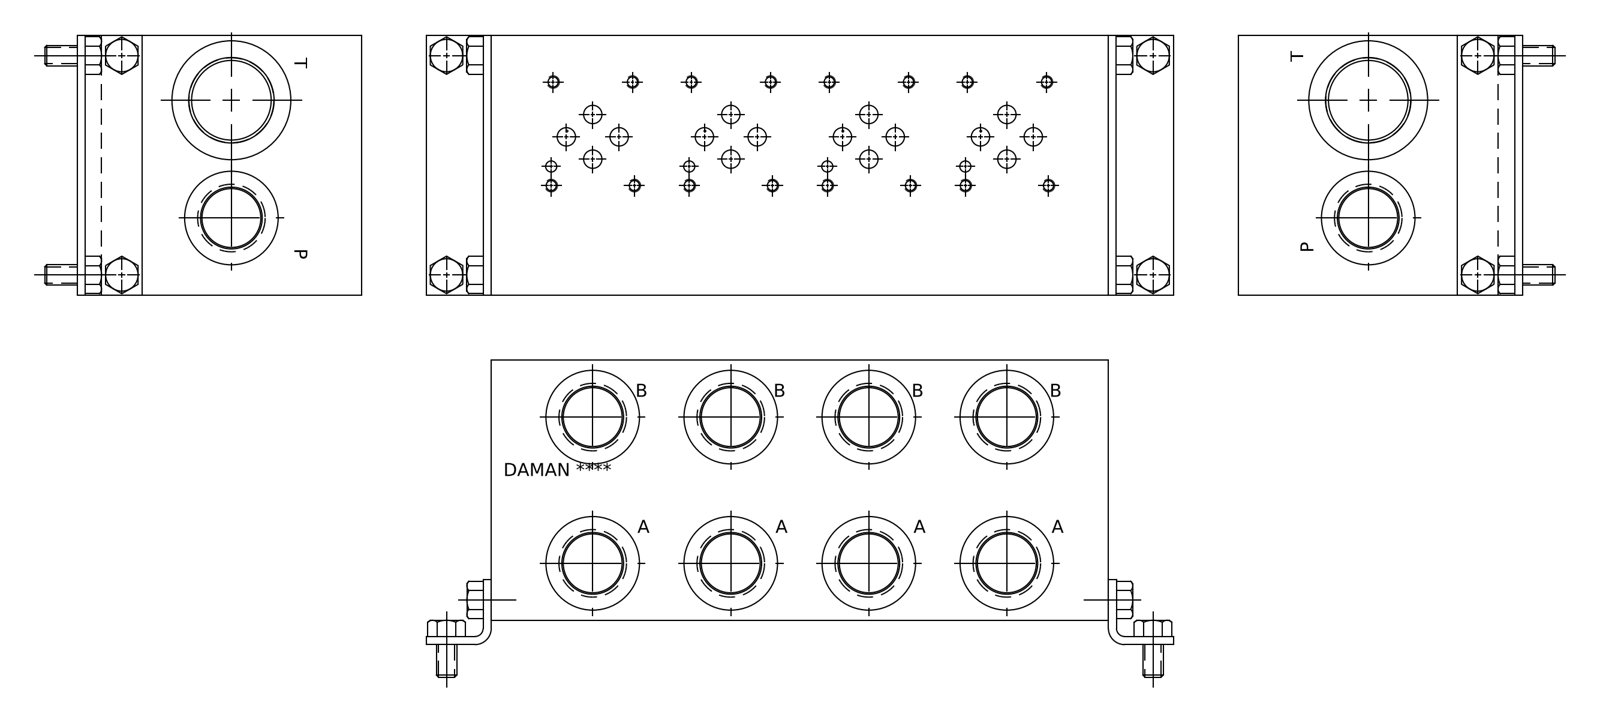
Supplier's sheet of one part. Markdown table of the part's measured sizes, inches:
| quantity | value |
| --- | --- |
| part name | Part_DD03HP042B_3D |
| STEP written by | Autodesk Inventor 2019 (AUTOMOTIVE_DESIGN) |
| units | inches |
| bodies | 1 solid, 770 faces (426 planar, 112 cylindrical, 232 other) |
| overall size | 9.5 × 4 × 4 |
| volume | 138.2 in³ |
| surface area | 244.2 in² |
| round holes (diameter × count) | 0.166 × 16, 0.197 × 16, 0.25 × 12, 0.906 × 9, 0.961 × 9, 1.045 × 9, 1.461 × 9, 0.156 × 4, 0.281 × 4, 0.422 × 4, 0.266 × 2, 0.315 × 2 |
| main face-to-face distances | 4, 9.5, 0.031, 3.969, 9.469, 9.438, 0.704, 0.673, 3.296, 0.039 |
| hole center spacings | 2.125, 4.25, 2.125, 0.868, 1.594, 2.026, 1.313, 1.393 |
